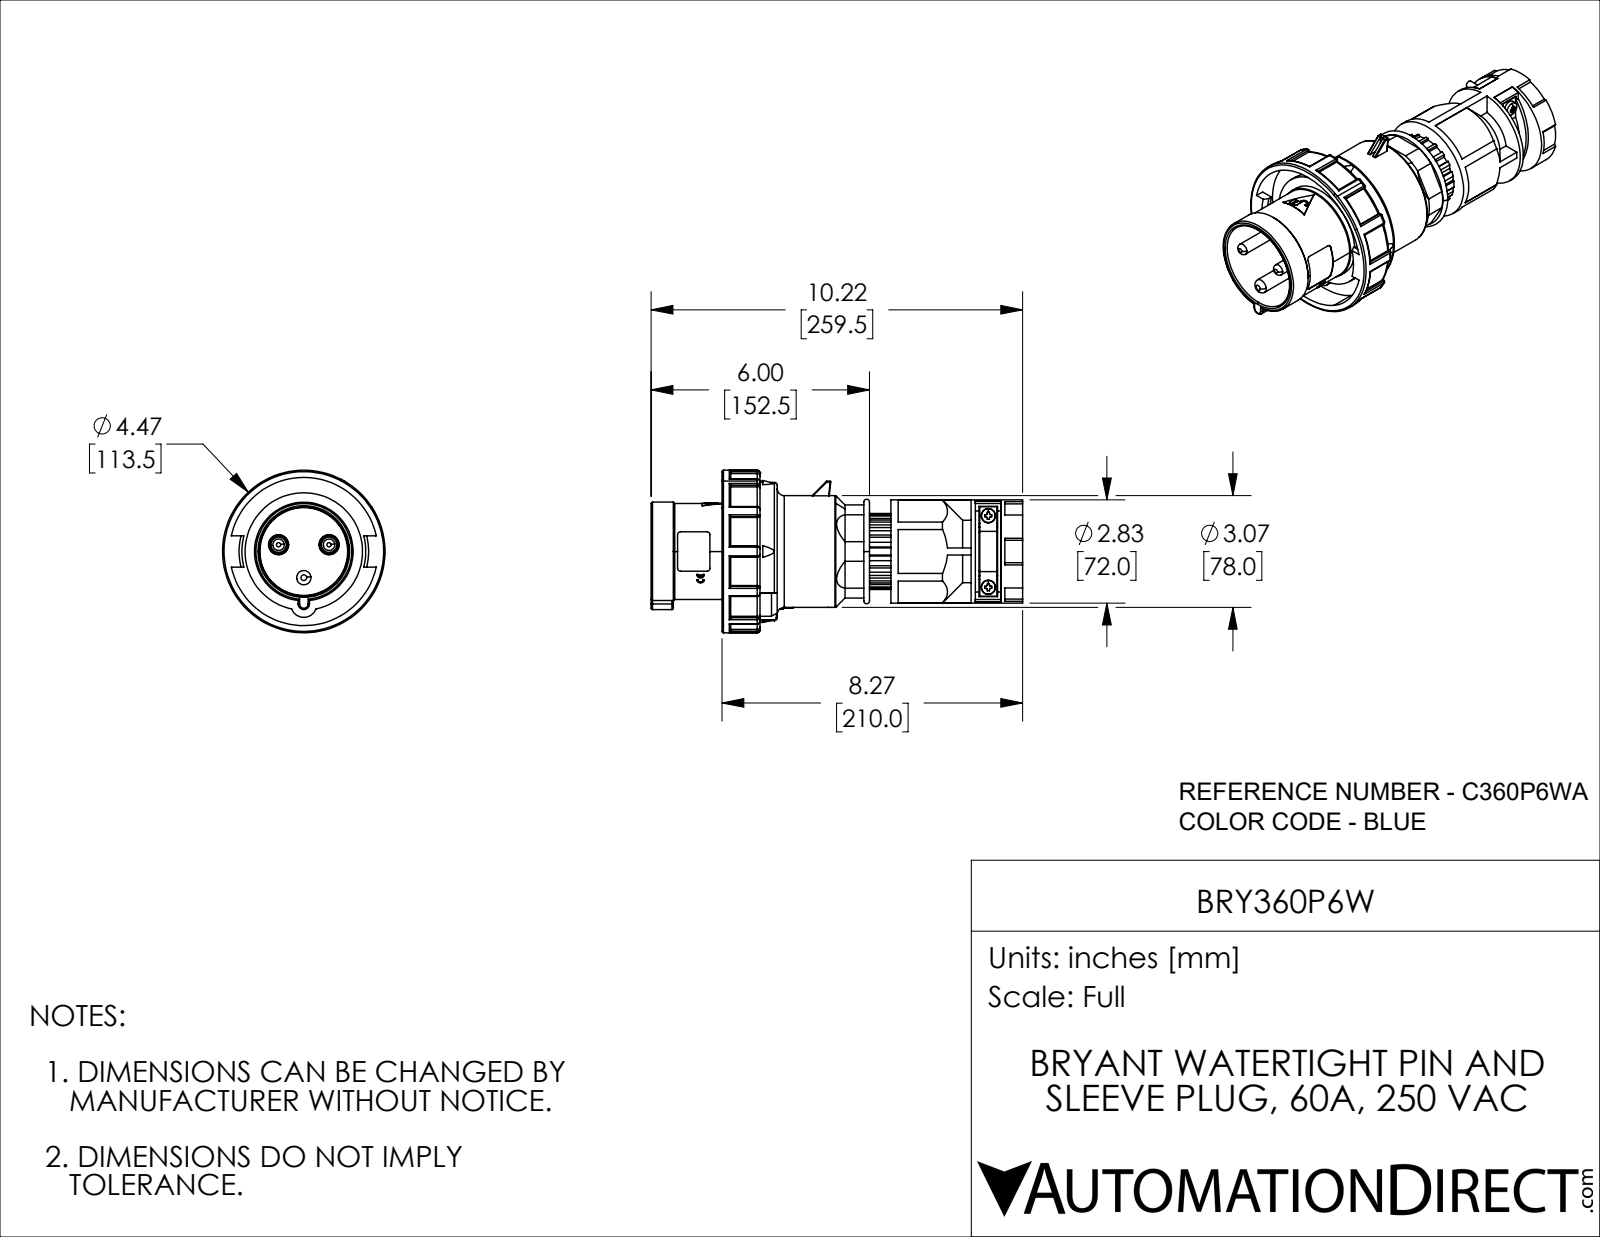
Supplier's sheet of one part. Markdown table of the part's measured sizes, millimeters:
| quantity | value |
| --- | --- |
| part name | BRY360P6W |
| STEP written by | SolidWorks 2021 (CONFIG_CONTROL_DESIGN) |
| units | millimeters |
| bodies | 7 solids, 1160 faces (486 planar, 384 cylindrical, 290 other) |
| overall size | 259.5 × 113.5 × 113.5 |
| volume | 766 329 mm³ |
| surface area | 150 850 mm² |
| round holes (diameter × count) | 2 × 2, 5 × 2, 37 × 1, 62 × 1, 65.5 × 1, 103.5 × 1 |
| round bosses / shafts (diameter × count) | 8 × 2, 113.5 × 1, 82 × 1, 78 × 1, 72 × 1, 68.9 × 1, 68.03 × 1, 67 × 1 |
| partial cylindrical surfaces (radius × count) | 1 × 34, 0.5 × 23, 2 × 18, 34.5 × 6, 0.4 × 4, 3 × 3, 4 × 3, 1.2 × 2 |
| main face-to-face distances | 160, 65, 101, 59, 5, 18, 3, 15, 77, 26 |
| hole center spacings | 50 |
